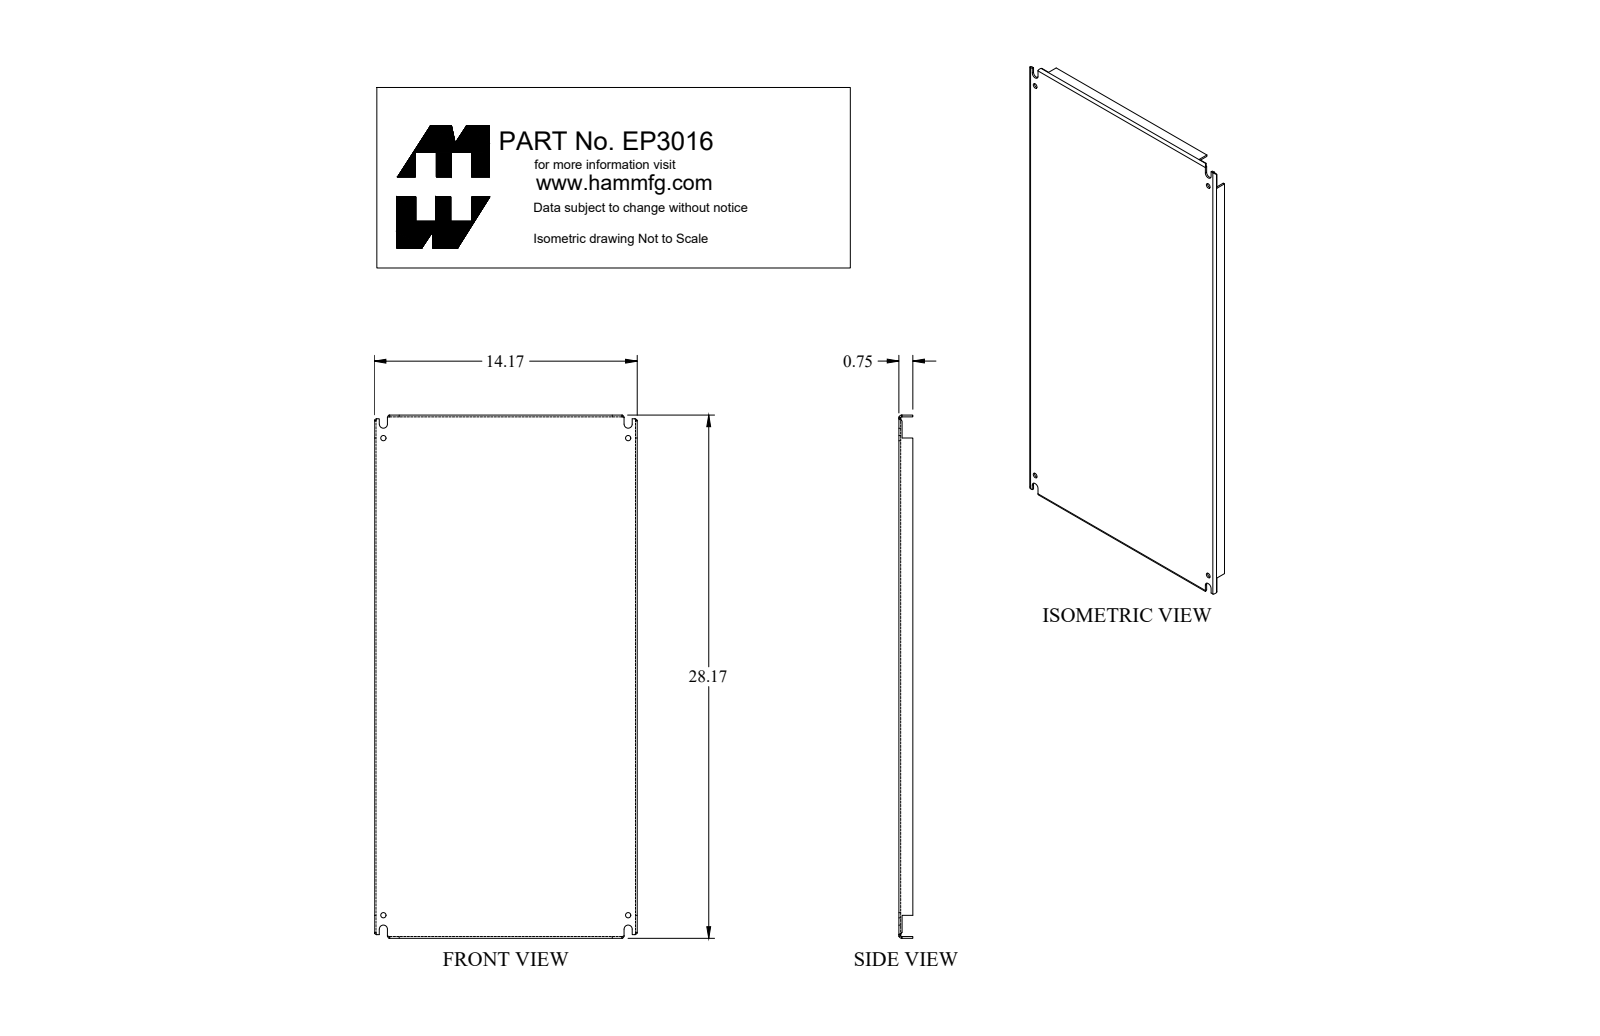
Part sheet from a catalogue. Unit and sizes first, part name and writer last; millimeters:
Units: millimetres
Overall size (bounding box): 715.5 × 359.9 × 19.1
Round holes (diameter × count): ⌀7.1 ×4
Partial cylindrical surfaces — rounded edges, fillets, slot ends (radius × count): R5.6 ×4, R1.2 ×2, R1.6 ×2, R3.6 ×2
Main face-to-face distances: 2.4, 357.5, 355.1, 359.9, 19.1, 16.6, 715.5, 4.3, 1.9, 14.7
Hole centre spacings: 335, 652.5, 733.5
Volume: 668 100 mm³ · Surface area: 559 400 mm²
Bodies: 1 solid, 84 faces (50 planar, 26 cylindrical, 8 other)
Part name (STEP PRODUCT): EP3016
STEP written by: SolidWorks 2018 (AUTOMOTIVE_DESIGN)
